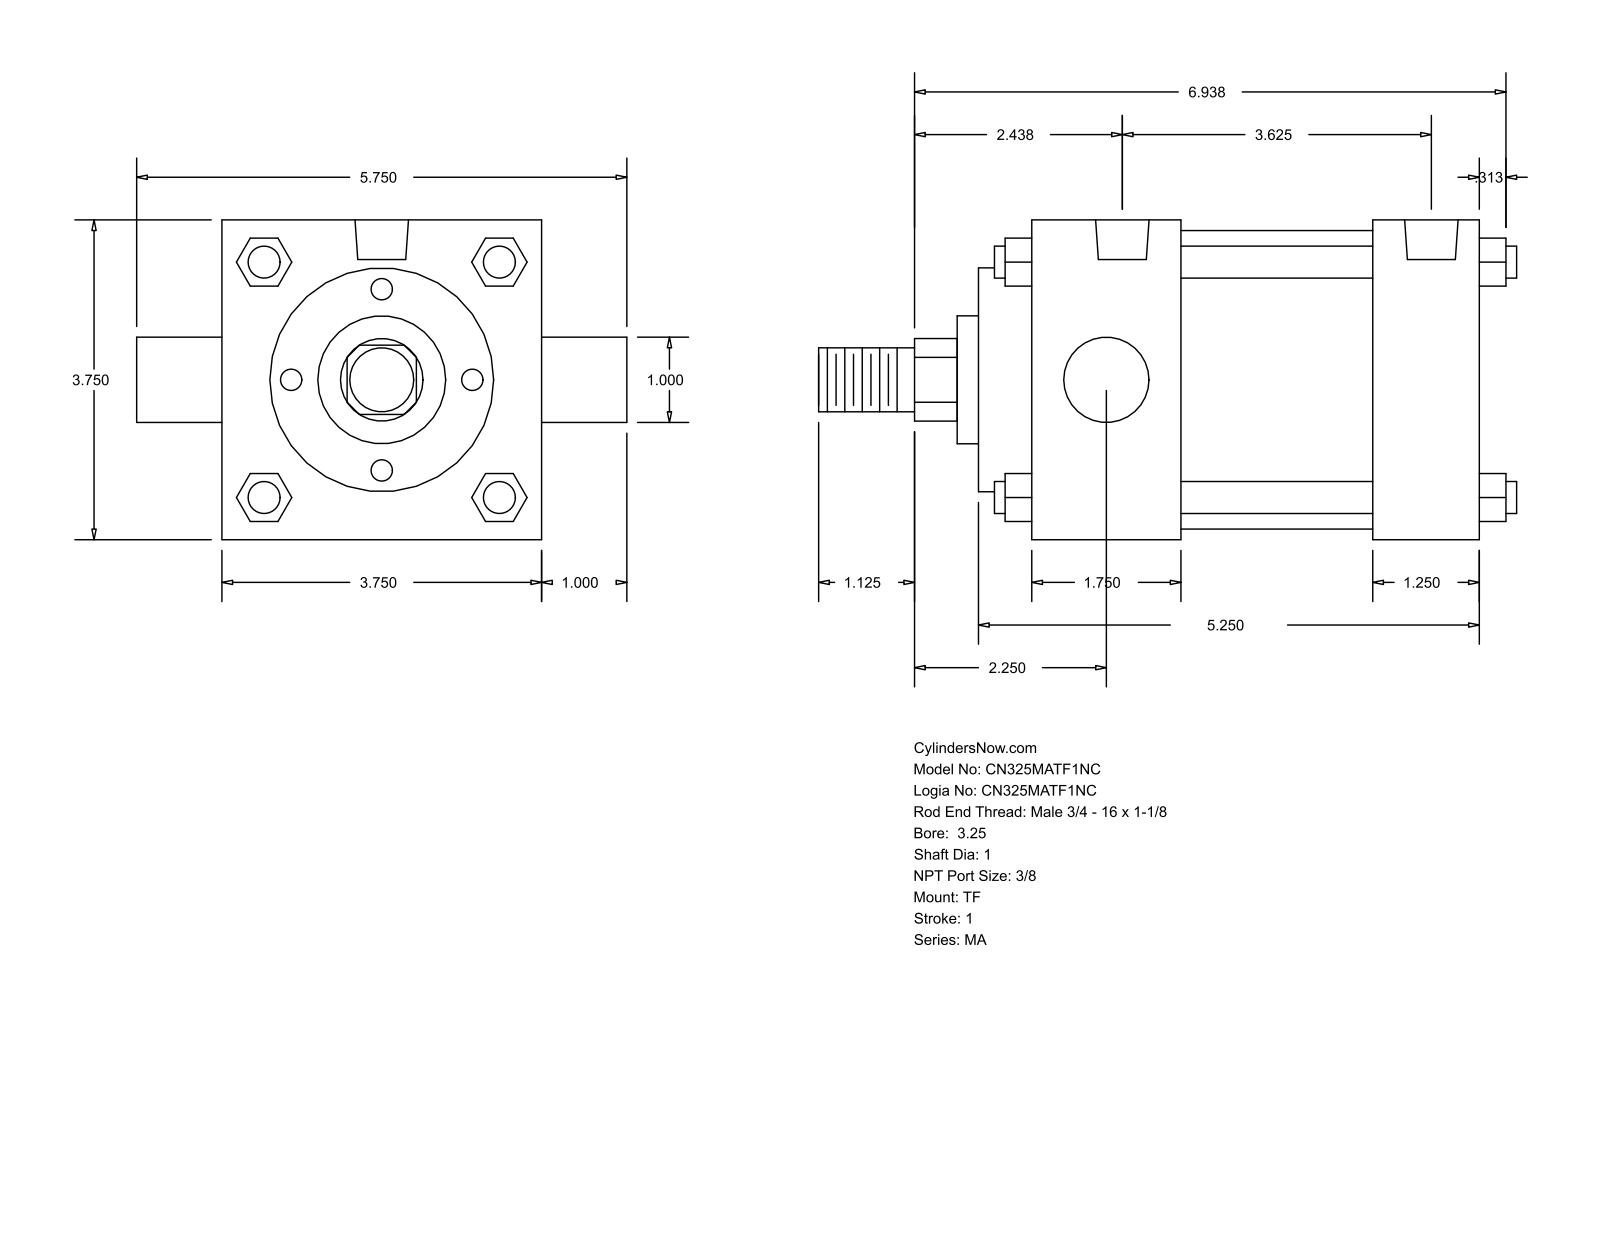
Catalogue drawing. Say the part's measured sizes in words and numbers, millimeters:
The part is named "MA_TF__0325_1". Its 3-D file was written by "GSSL Pune (CONFIG_CONTROL_DESIGN)". It is 0 solids with 122 faces: 93 planar, 29 cylindrical and 0 other. Overall it measures 207.96 by 146.05 by 95.25 millimeters. Round holes: 3 of diameter 11.11, 2 of diameter 15.93. Round bosses or shafts: 4 of diameter 9.53, 2 of diameter 25.4, 1 of diameter 88.9, 1 of diameter 66.67, 1 of diameter 38.1, 1 of diameter 19.05. Partial cylindrical surfaces (rounded edges, fillets, slot ends): 1 of radius 12.29. The main face-to-face distances are 95.24, 133.36, 44.46, 101.61, 57.15, 88.9, 31.75, 15.87, 60.33, 117.48. The hole center spacings are 4.76, 4.77, 82.55, 87.31, 87.32, 92.08.
